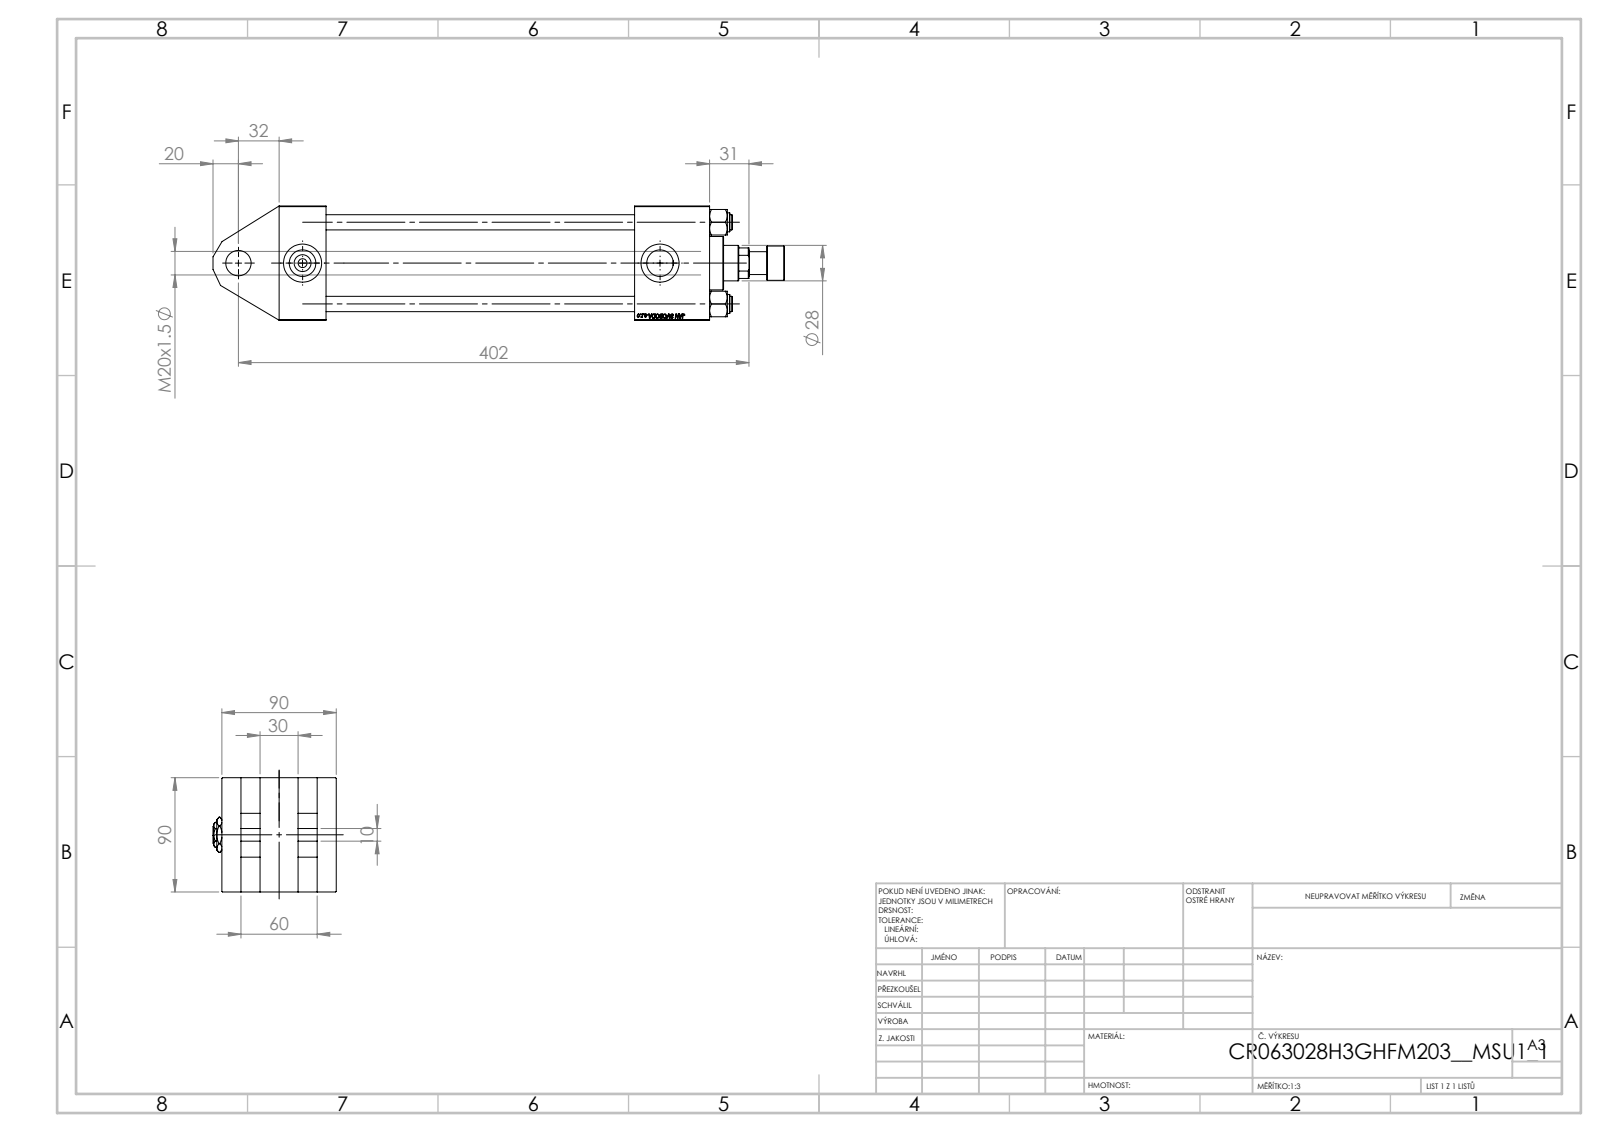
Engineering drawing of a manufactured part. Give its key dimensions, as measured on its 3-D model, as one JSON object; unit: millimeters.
{"part_name": "V215_VC_A; Zatka_pro_OIL_PORT; NUT_M5_H; V215CR_VCP_H (+3 more)", "step_written_by": "SolidWorks 2019 (CONFIG_CONTROL_DESIGN)", "units": "millimeters", "bodies": {"solids": 14, "faces": 1244, "planar": 570, "cylindrical": 98, "other": 576}, "overall_size": [450, 97, 90], "volume_mm3": 1354000, "surface_area_mm2": 324800, "round_holes": [[12, 4], [7, 2], [20.96, 2], [30, 2], [18.5, 1], [20, 1], [28, 1], [31, 1], [50, 1], [60, 1], [63, 1]], "round_bosses_or_shafts": [[15, 4], [69, 1], [42, 1], [27, 1], [18, 1]], "face_to_face_distances": [90, 15, 60, 30, 302, 45, 37, 59, 75, 339], "hole_center_spacings": [45.47, 64.3, 90.93, 50.5, 281.5, 332]}
